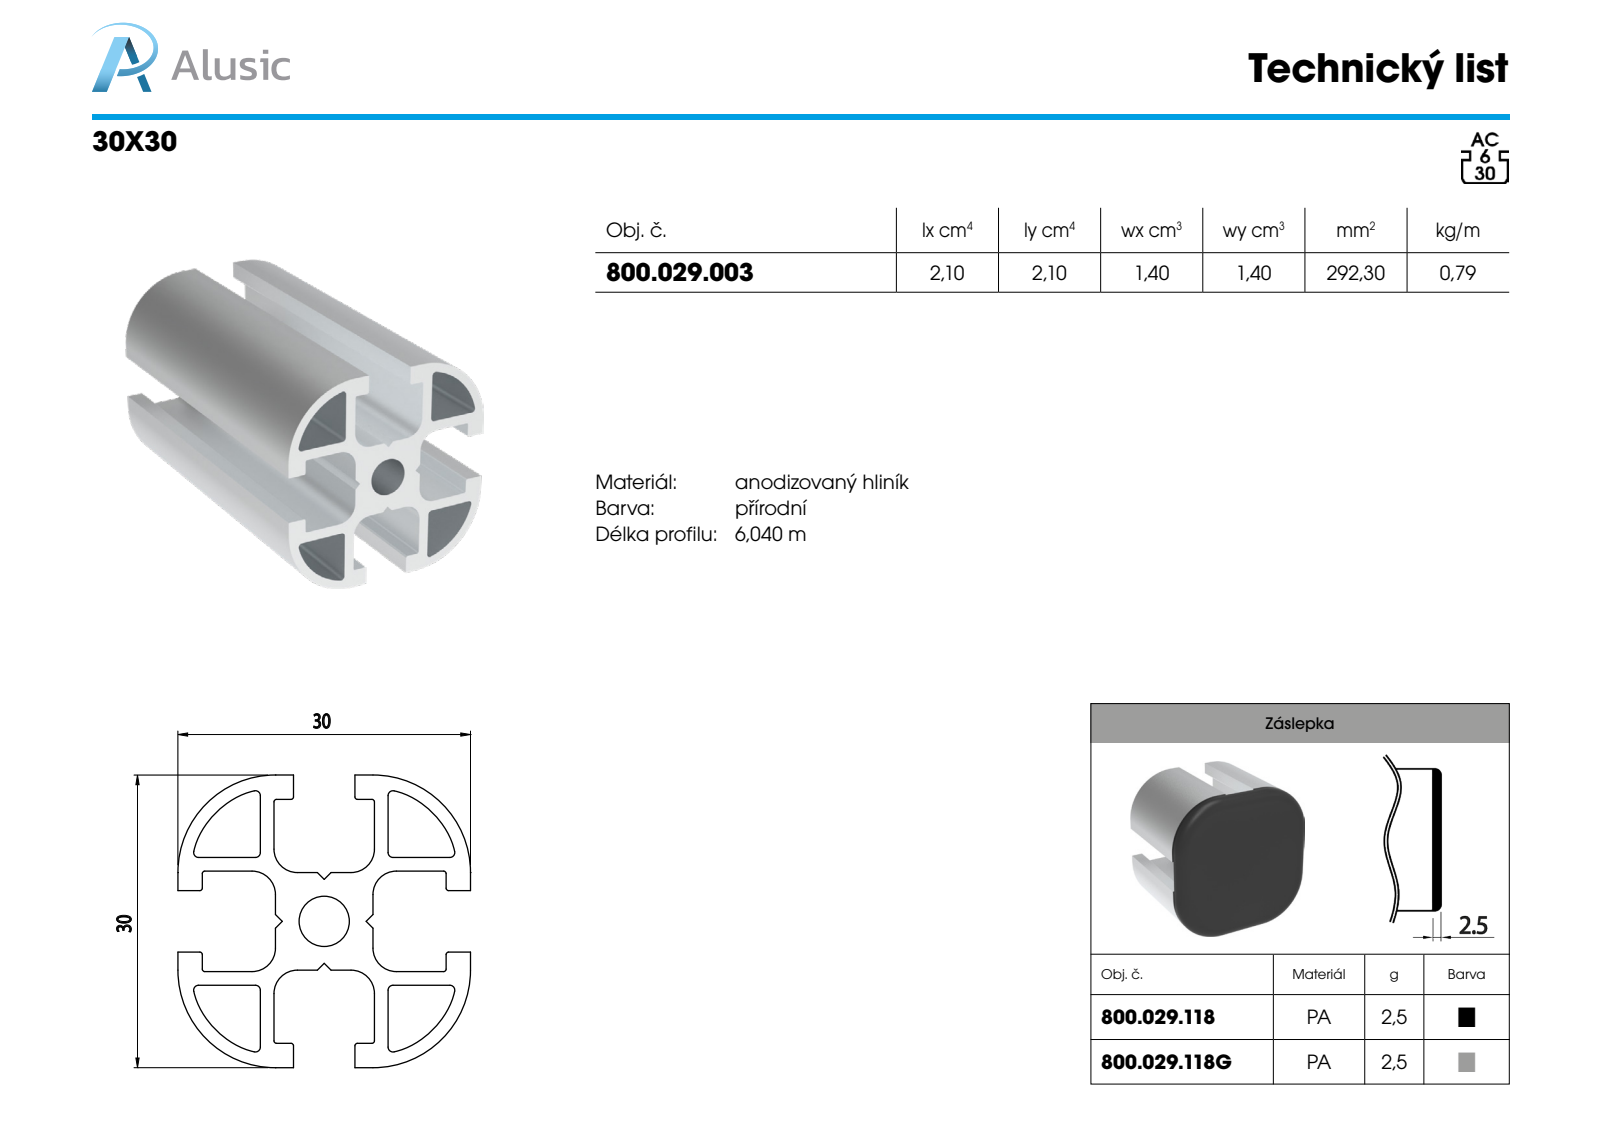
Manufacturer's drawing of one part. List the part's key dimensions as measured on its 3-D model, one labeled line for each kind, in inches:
Part name (STEP PRODUCT): 800.029.118
STEP written by: SolidWorks 2012 (CONFIG_CONTROL_DESIGN)
Units: inches
Bodies: 1 solid, 69 faces (23 planar, 29 cylindrical, 17 other)
Overall size (bounding box): 1.181 × 1.181 × 0.335
Volume: 0.136 in³ · Surface area: 3.867 in²
Round holes (diameter × count): ⌀0.138 ×4
Round bosses / shafts (diameter × count): ⌀0.197 ×4
Partial cylindrical surfaces — rounded edges, fillets, slot ends (radius × count): R0.079 ×4, R0.394 ×4, R0.102 ×1
Main face-to-face distances: 0.098, 0.047, 0.567, 0.614, 0.236, 0.335, 1.181, 0.079, 0.157, 0.256
Hole centre spacings: 0.735, 1.04
